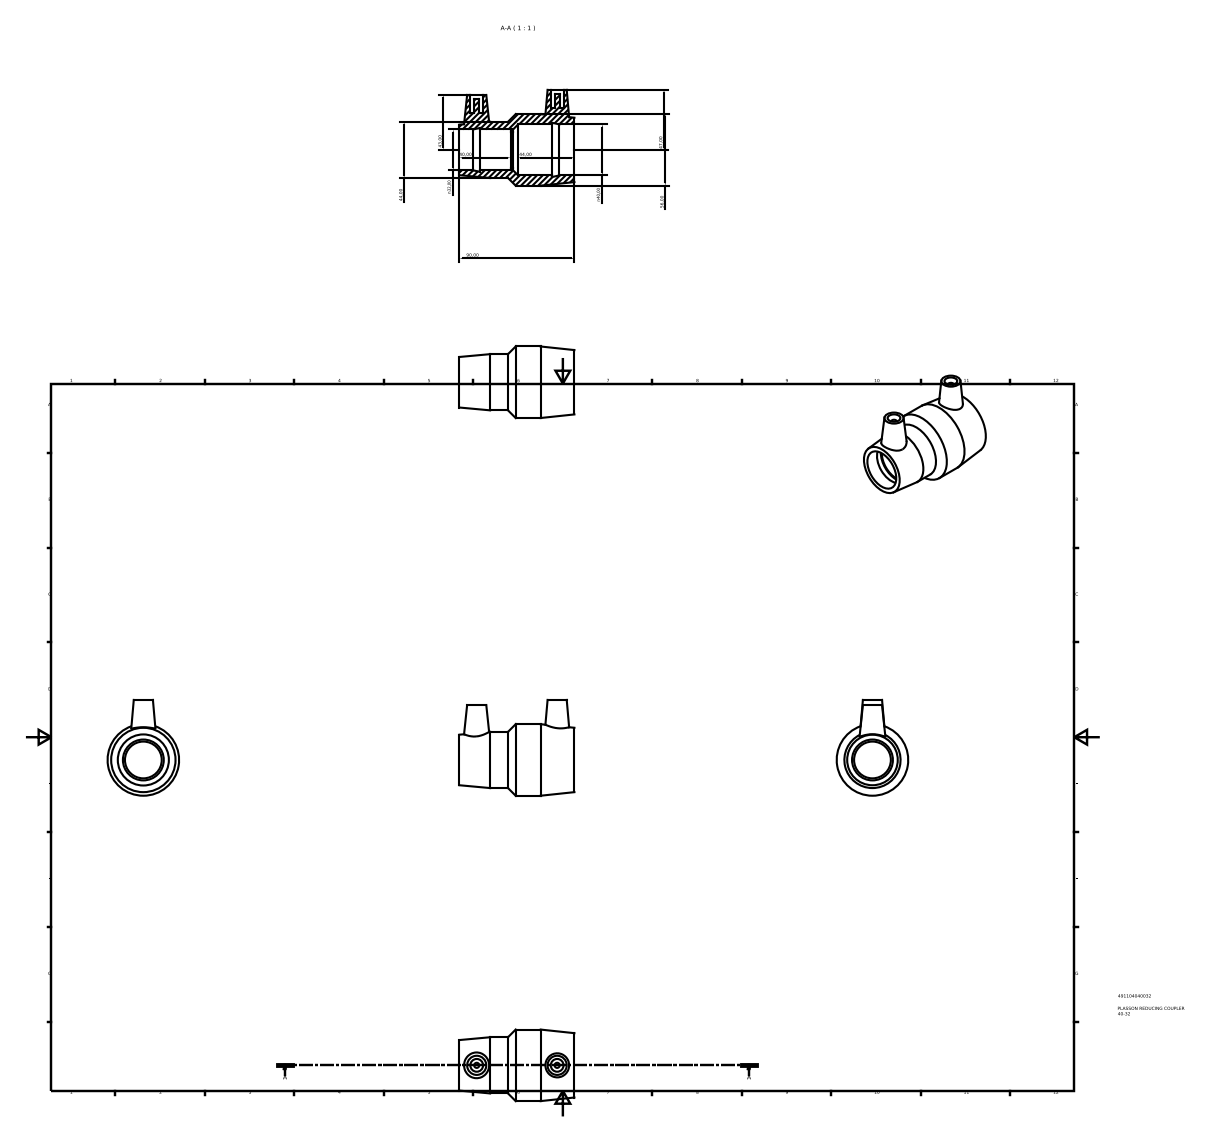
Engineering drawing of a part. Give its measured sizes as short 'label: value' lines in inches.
name: 491104040032
written by: Autodesk Inventor 2015 (AUTOMOTIVE_DESIGN)
unit: in
bodies: 1 solid, 31 faces (12 planar, 11 cylindrical, 8 other)
size: 3.543 × 2.953 × 2.205
volume: 5.344 in³; area: 46.23 in²
holes: 2× ⌀0.394, 1× ⌀1.134, 1× ⌀1.26, 1× ⌀1.575
bosses: 2× ⌀0.157, 1× ⌀2.205, 1× ⌀1.732
face distances: 3.543, 0.157, 2.85, 0.693, 1.654, 1.197, 1.89, 1.575, 0.079, 1.276
hole spacings: 2.48
